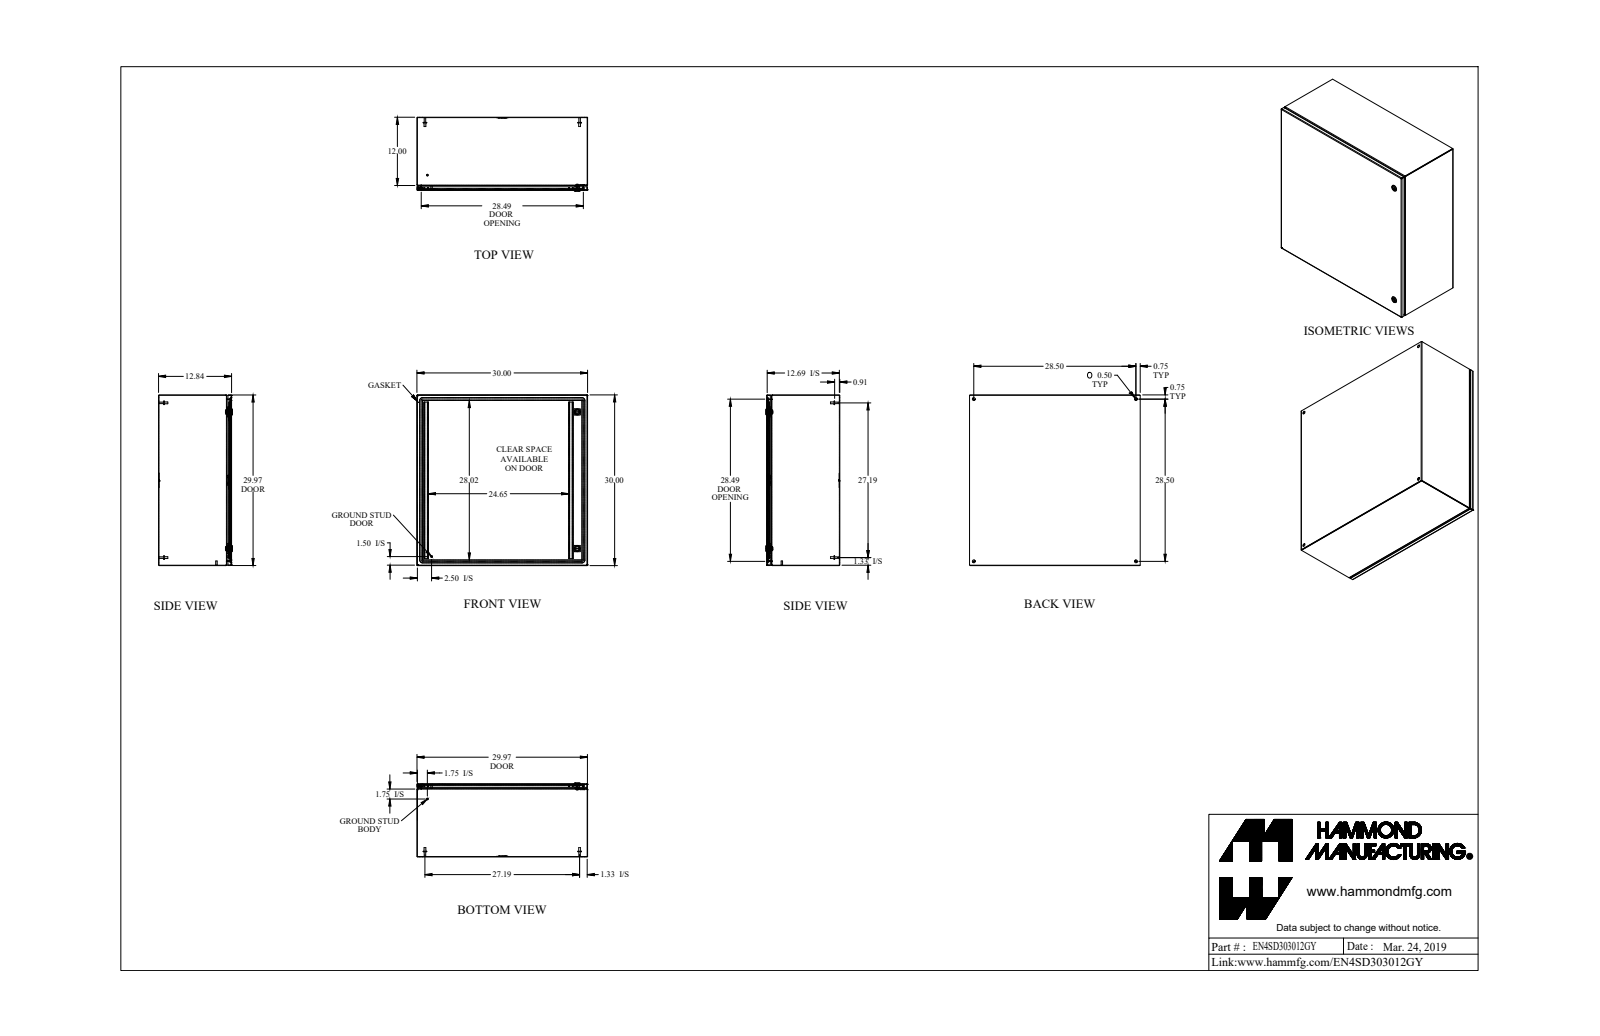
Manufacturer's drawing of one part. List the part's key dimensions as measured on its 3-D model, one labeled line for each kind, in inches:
Part name (STEP PRODUCT): EN4SD303012GY
STEP written by: SolidWorks 2019 (AUTOMOTIVE_DESIGN)
Units: inches
Bodies: 33 solids, 837 faces (399 planar, 282 cylindrical, 156 other)
Overall size (bounding box): 30 × 30 × 12.997
Volume: 265.2 in³ · Surface area: 7 431 in²
Round holes (diameter × count): ⌀0.5 ×4, ⌀0.232 ×2, ⌀0.625 ×2, ⌀0.785 ×2, ⌀0.172 ×1, ⌀0.24 ×1, ⌀0.242 ×1
Round bosses / shafts (diameter × count): ⌀0.625 ×4, ⌀0.313 ×4, ⌀0.27 ×4, ⌀1.1 ×2, ⌀0.525 ×2, ⌀0.281 ×2, ⌀0.25 ×2, ⌀0.455 ×1
Partial cylindrical surfaces — rounded edges, fillets, slot ends (radius × count): R0.108 ×22, R0.036 ×14, R0.043 ×12, R0.081 ×12, R0.312 ×12, R0.006 ×6, R0.062 ×6, R0.125 ×4
Main face-to-face distances: 0.072, 12.765, 29.928, 12.693, 12.837, 29.856, 30, 0.837, 11.928, 0.75
Hole centre spacings: 28.5, 27.519, 40.305, 2.493, 2.494, 23.999, 26.271, 26.272
